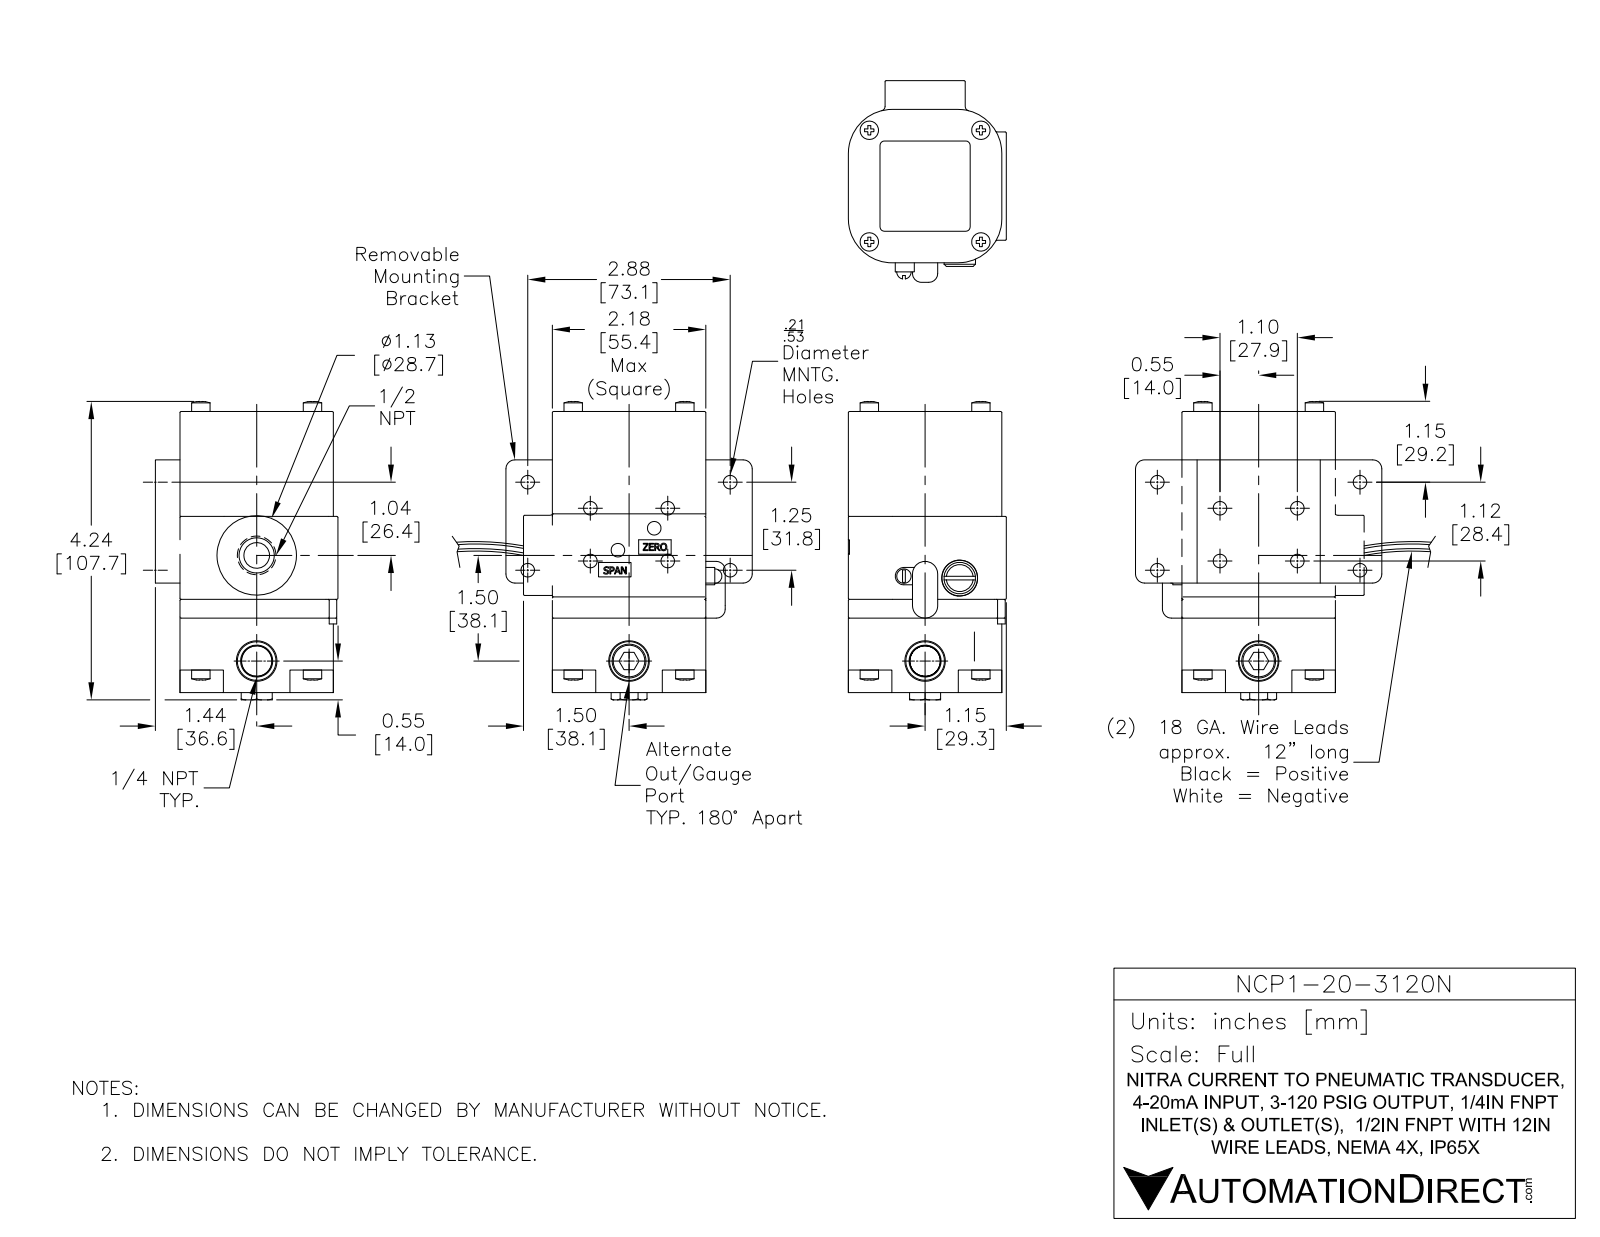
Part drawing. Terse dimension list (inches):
name: NCP1-20-3120N
written by: SolidWorks 2016 (AUTOMOTIVE_DESIGN)
unit: in
bodies: 11 solids, 677 faces (371 planar, 143 cylindrical, 163 other)
size: 4.239 × 3.5 × 2.613
volume: 16.83 in³; area: 64.46 in²
holes: 8× ⌀0.203, 2× ⌀0.13, 2× ⌀0.188, 1× ⌀0.422, 1× ⌀0.493, 1× ⌀0.688
bosses: 4× ⌀0.255, 1× ⌀1.13, 1× ⌀0.469, 1× ⌀0.436, 1× ⌀0.24
rounds: 26× R0.016, 10× R0.125, 8× R0.063, 6× R0.609, 4× R0.313, 2× R0.018, 2× R0.12, 2× R0.175
face distances: 0.063, 0.266, 2.125, 0.203, 0.328, 3.995, 2.535, 2.472, 2.269, 2.206
hole spacings: 0.75, 1.125, 1.313, 2.037, 2.937, 3.217, 0.012, 0.013
